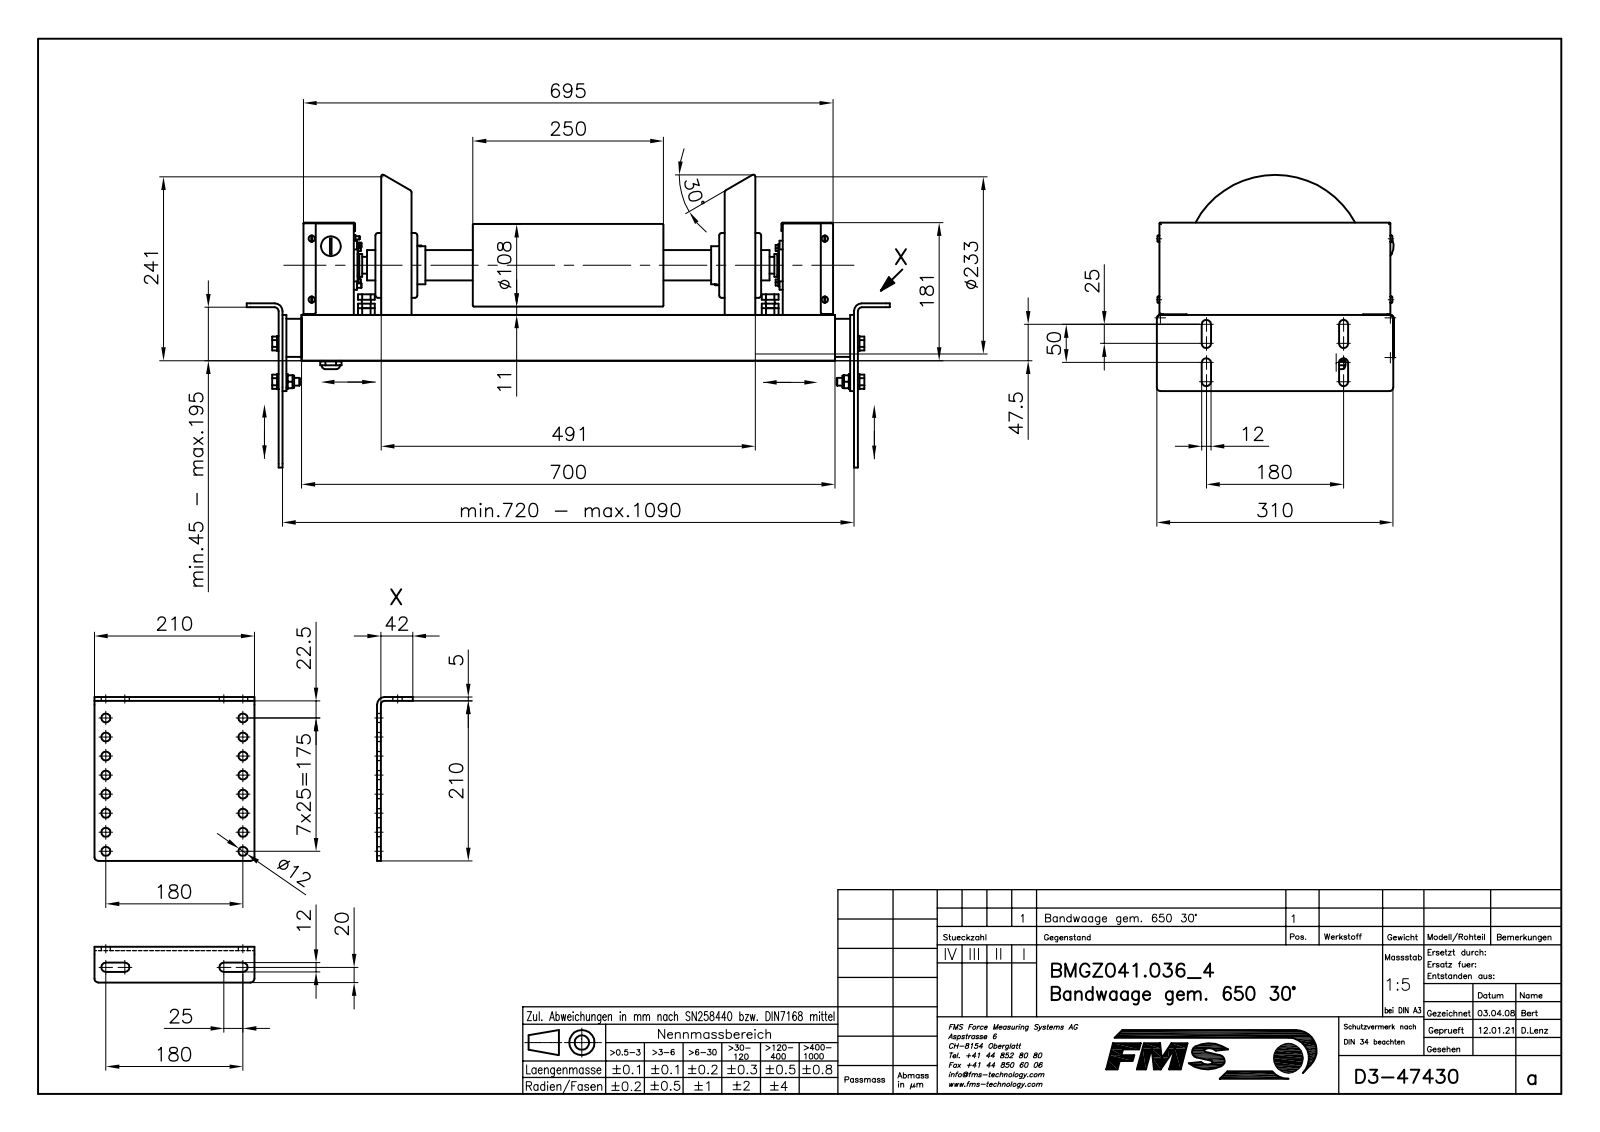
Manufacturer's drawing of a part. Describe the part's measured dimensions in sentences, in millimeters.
The part is named "B47430_STP; B50029; B46957; B4695602 (+8 more)". Its 3-D file was written by "Mechanical Desktop 2009 (CONFIG_CONTROL_DESIGN)". It is 161 solids with 2732 faces: 1379 planar, 974 cylindrical and 379 other. Overall it measures 844 by 383.76 by 310.7 millimeters. Its volume is 6 640 000 cubic millimeters and its surface area 3 245 000 square millimeters. Round holes: 17 of diameter 12, 6 of diameter 5, 4 of diameter 3.5, 4 of diameter 4.9, 4 of diameter 6.4, 4 of diameter 8.68, 4 of diameter 8.75, 4 of diameter 10, 4 of diameter 10.5, 4 of diameter 10.68, 4 of diameter 14.8, 3 of diameter 4.1. Round bosses or shafts: 11 of diameter 12, 8 of diameter 8.2, 8 of diameter 4.2, 6 of diameter 20, 6 of diameter 10, 5 of diameter 5, 4 of diameter 16, 4 of diameter 11.1. Partial cylindrical surfaces (rounded edges, fillets, slot ends): 34 of radius 2, 24 of radius 1, 16 of radius 4, 16 of radius 5, 14 of radius 6, 8 of radius 3.5, 6 of radius 2.25, 4 of radius 0.5. The main face-to-face distances are 4, 5, 1, 270, 36, 266, 32, 56, 274, 40. The hole center spacings are 25, 181.73, 50, 186.82, 75, 195, 100, 180.
